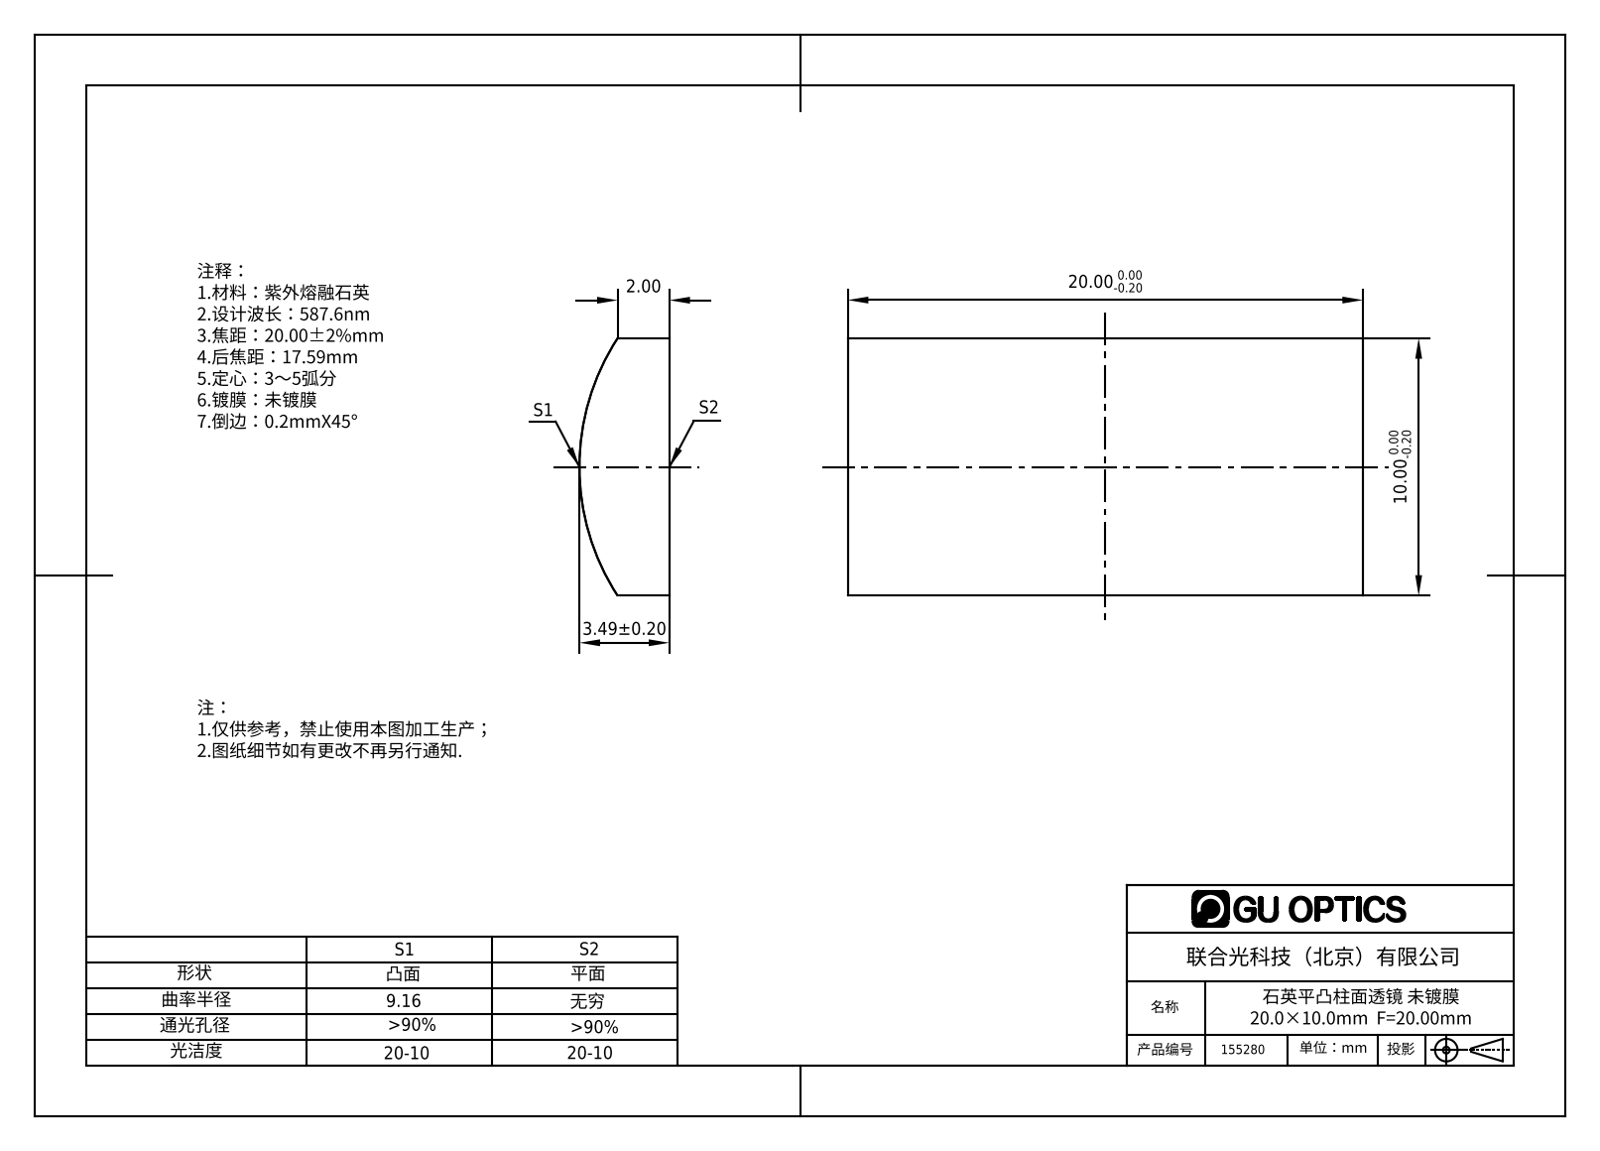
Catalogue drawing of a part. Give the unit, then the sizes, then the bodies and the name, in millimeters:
Units: millimetres
Overall size (bounding box): 20 × 10 × 3.49
Partial cylindrical surfaces — rounded edges, fillets, slot ends (radius × count): R9.16 ×1
Main face-to-face distances: 10, 20
Volume: 602 mm³ · Surface area: 552 mm²
Bodies: 1 solid, 6 faces (5 planar, 1 cylindrical, 0 other)
Part name (STEP PRODUCT): 155280
STEP written by: SolidWorks 2016 (AUTOMOTIVE_DESIGN)
